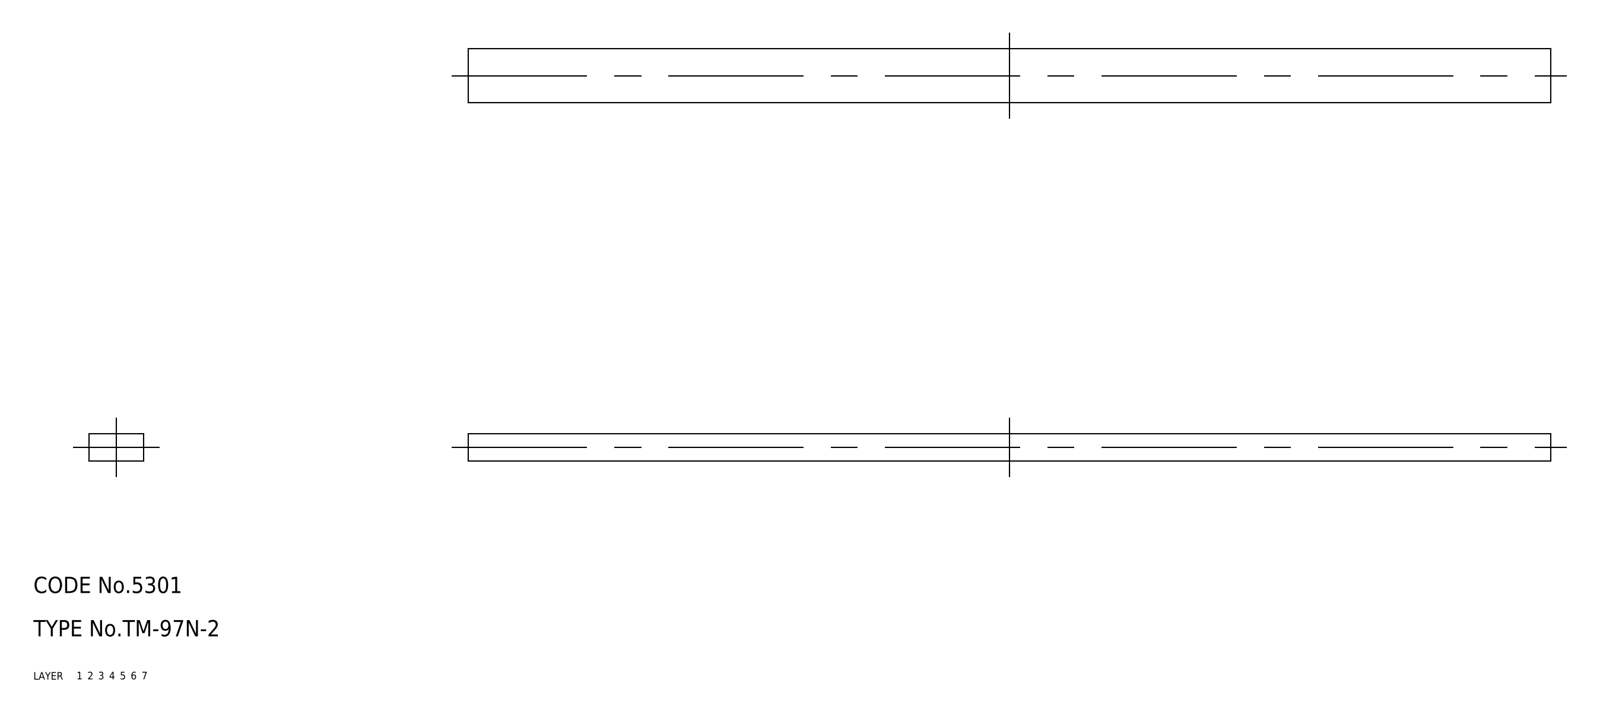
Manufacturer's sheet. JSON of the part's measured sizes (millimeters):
{"part_name": "rubber foam", "step_written_by": "CADfix (AUTOMOTIVE_DESIGN)", "units": "millimeters", "bodies": {"solids": 1, "faces": 6, "planar": 0, "cylindrical": 0, "other": 6}, "overall_size": [200, 10, 5], "volume_mm3": 10000, "surface_area_mm2": 6100}
